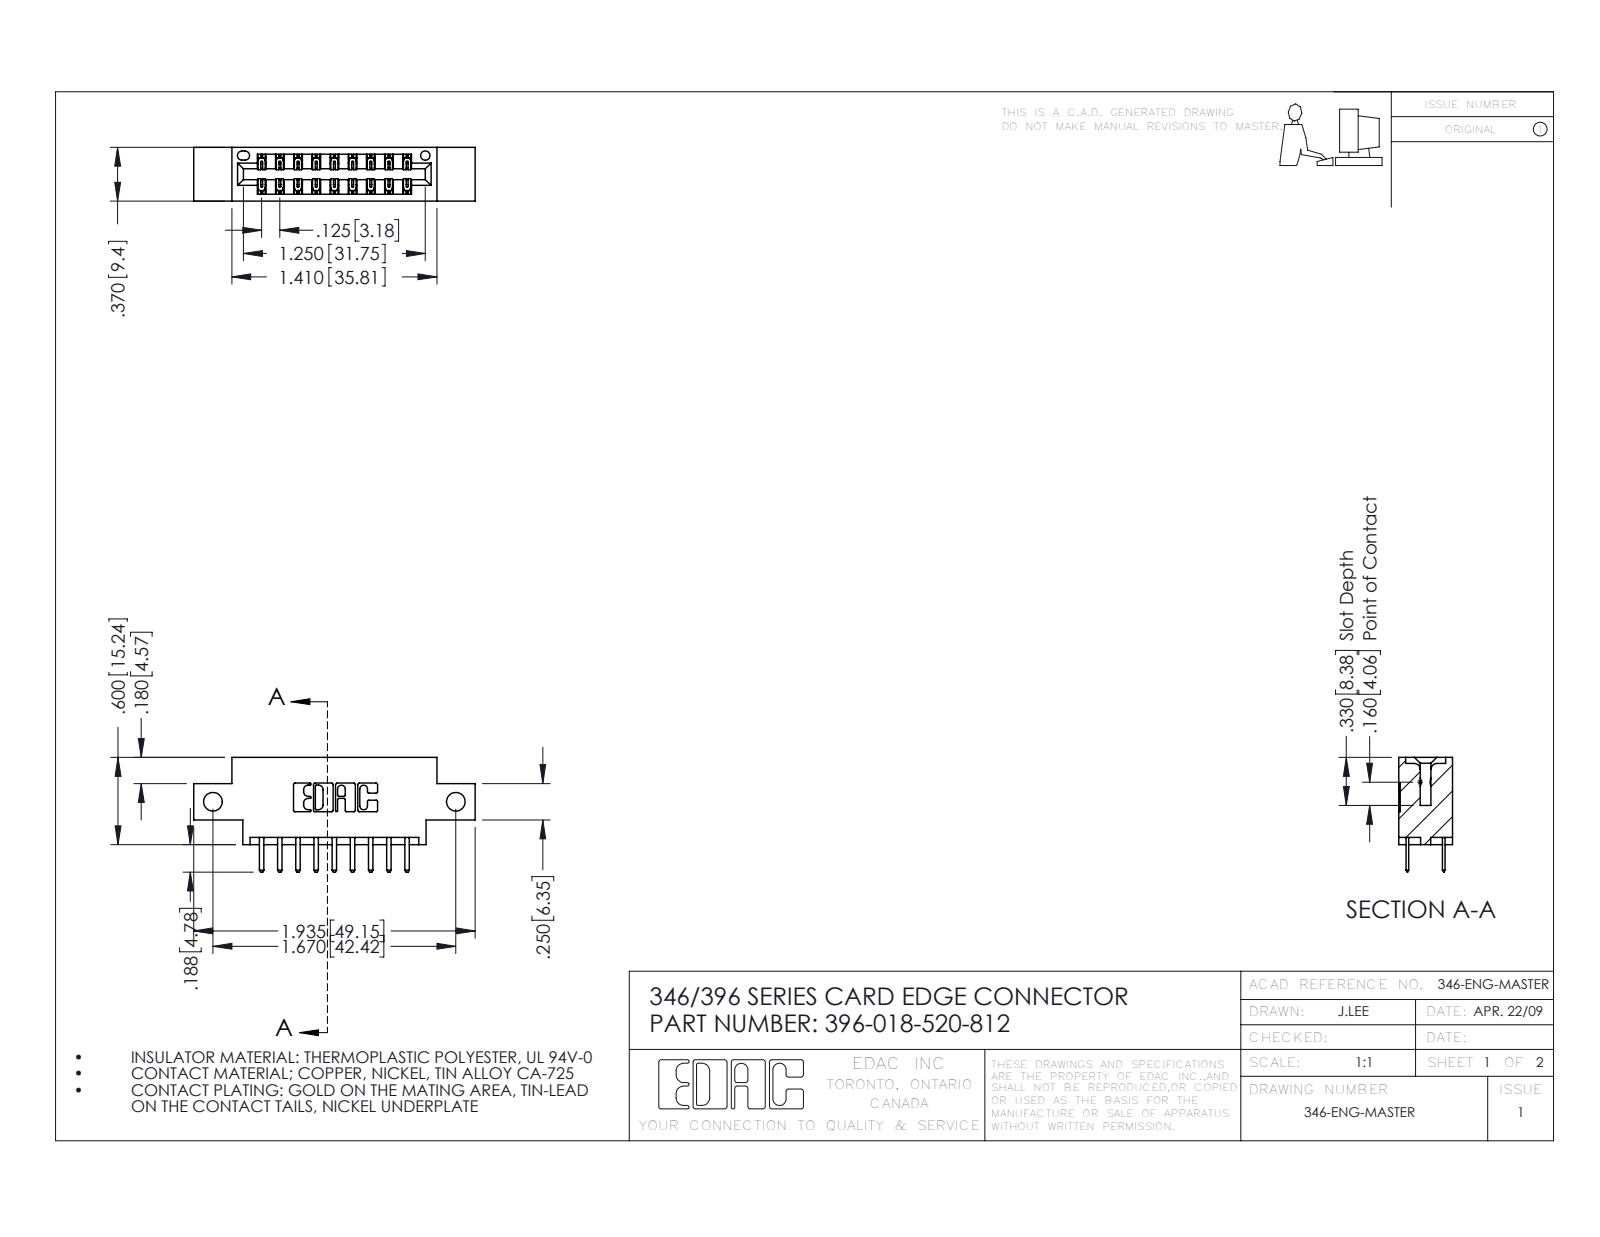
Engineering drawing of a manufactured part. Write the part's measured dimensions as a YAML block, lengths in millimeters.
part_name: "345-292-001_345-293-120; 346 Part_0.170 Offset - Side Mount; 396-018-520-812"
step_written_by: "SolidWorks 2016 (CONFIG_CONTROL_DESIGN)"
units: millimeters
bodies: {solids: 19, faces: 1134, planar: 746, cylindrical: 388, other: 0}
overall_size: [49.1, 20, 9.4]
volume: 4290
surface_area: 5397
round_holes:
  - {diameter: 3.3, count: 2}
  - {diameter: 1.6, count: 1}
partial_cylinders:
  - {radius: 0.2, count: 27}
  - {radius: 0.3, count: 22}
  - {radius: 0.3, count: 22}
  - {radius: 0.2, count: 6}
  - {radius: 0.8, count: 6}
  - {radius: 0.7, count: 3}
  - {radius: 0.4, count: 2}
  - {radius: 0.6, count: 2}
face_to_face_distances: [6.4, 9.4, 1.2, 8.2, 3.8, 5.6, 2.5, 4.4, 7, 1.8]
hole_center_spacings: [42.4]
